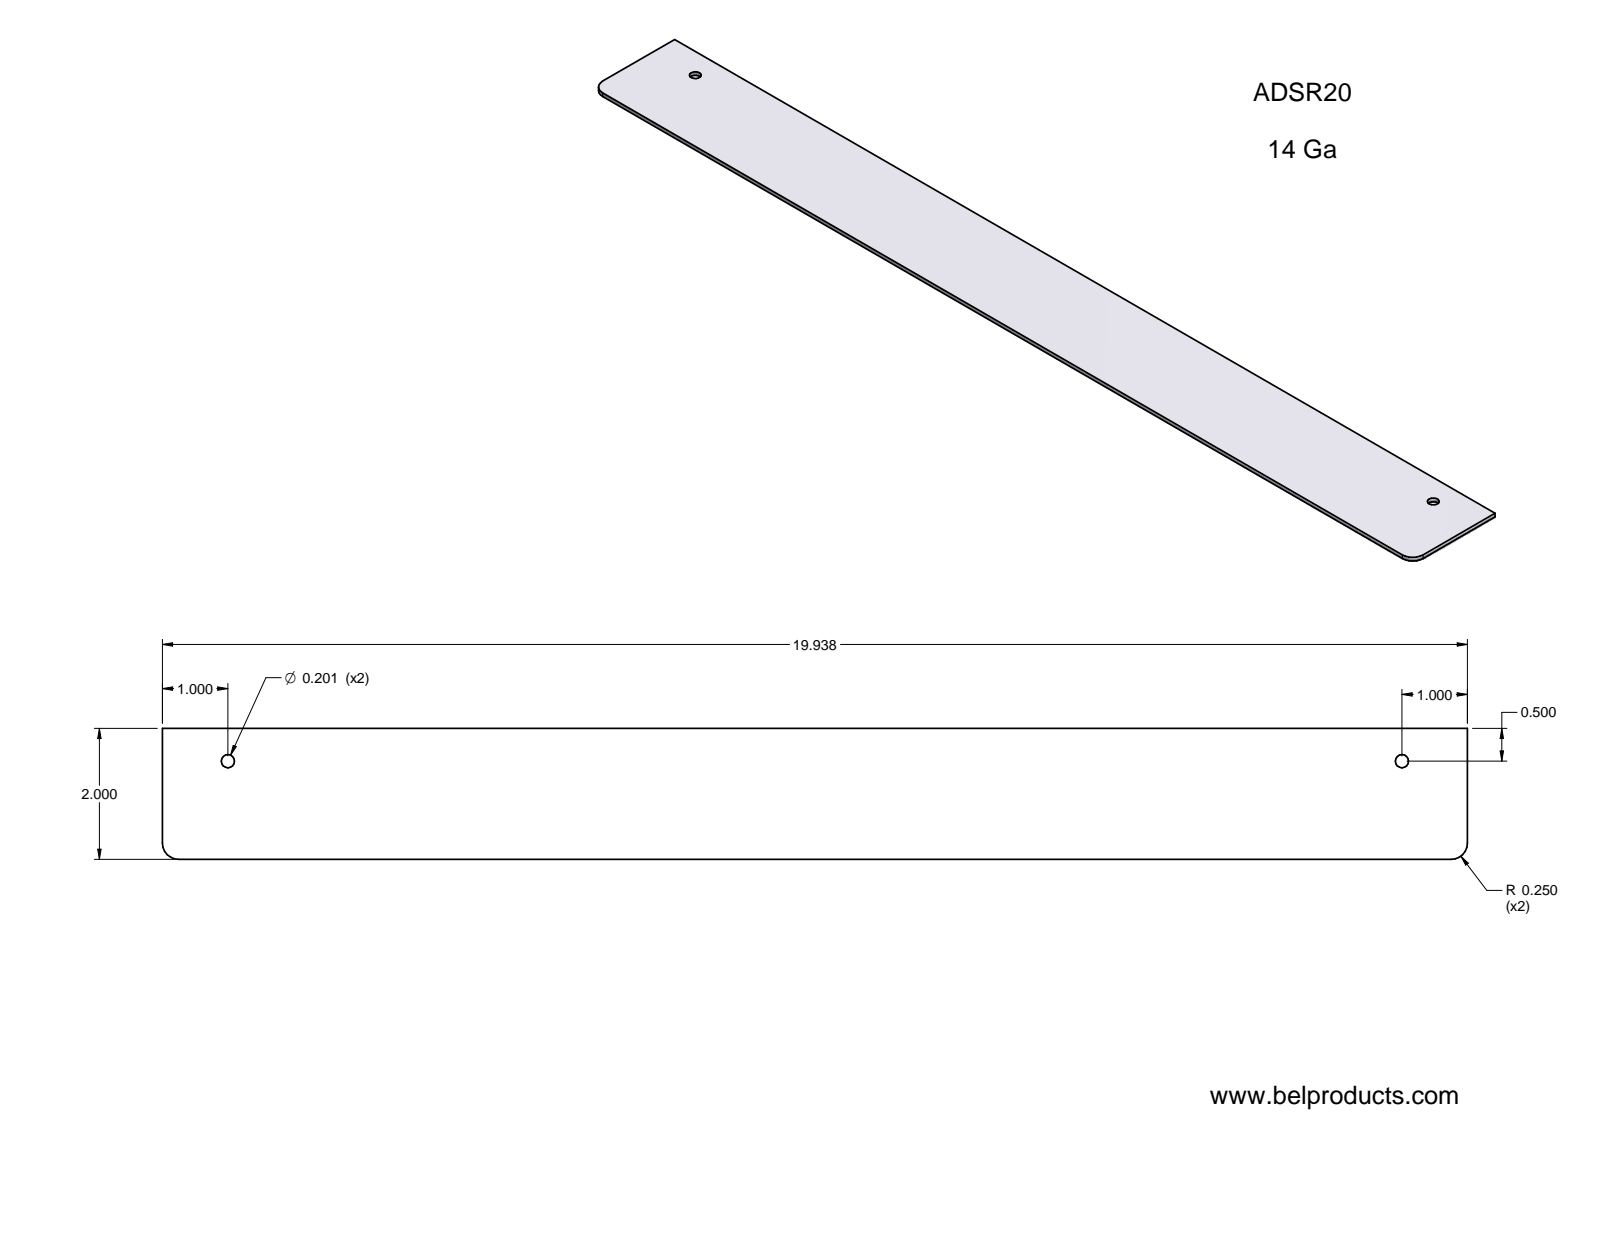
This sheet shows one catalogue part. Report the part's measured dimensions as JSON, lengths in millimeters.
{"step_written_by": "Unknown (AUTOMOTIVE_DESIGN)", "units": "millimeters", "bodies": {"solids": 1, "faces": 10, "planar": 6, "cylindrical": 4, "other": 0}, "overall_size": [506.41, 50.8, 1.91], "volume_mm3": 48897, "surface_area_mm2": 53509, "round_holes": [[5.11, 2]], "partial_cylinders_radius": [[6.35, 2]], "face_to_face_distances": [1.91, 50.8, 506.42], "hole_center_spacings": [455.62]}
